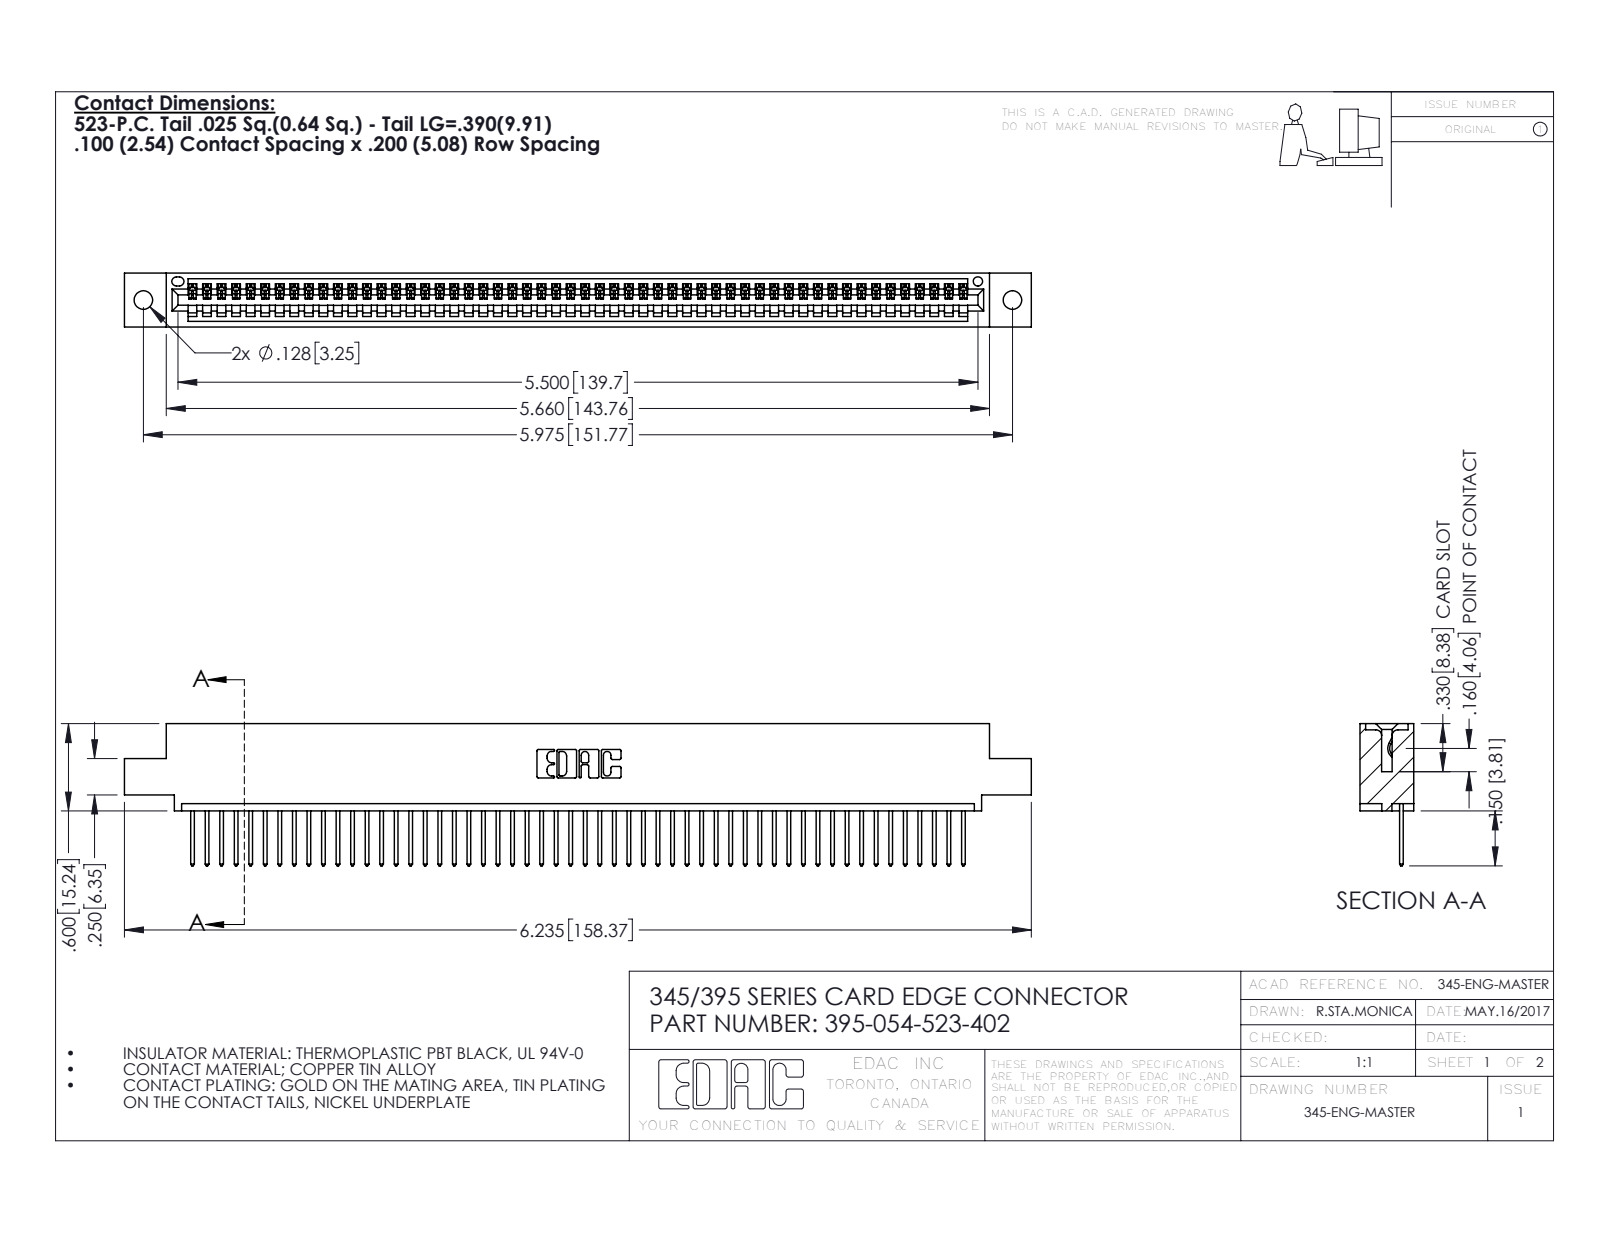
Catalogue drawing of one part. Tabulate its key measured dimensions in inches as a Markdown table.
| quantity | value |
| --- | --- |
| part name | 345-292-001_345-293-123; 395-054-523-402; 345 Part_0.110 Offset - 0.128 Dia |
| STEP written by | SolidWorks 2016 (CONFIG_CONTROL_DESIGN) |
| units | inches |
| bodies | 55 solids, 3262 faces (2244 planar, 1018 cylindrical, 0 other) |
| overall size | 6.235 × 0.977 × 0.37 |
| volume | 0.916 in³ |
| surface area | 30.97 in² |
| round holes (diameter × count) | 0.128 × 2, 0.064 × 1 |
| partial cylindrical surfaces (radius × count) | 0.006 × 108, 0.01 × 108, 0.01 × 22, 0.007 × 6, 0.031 × 6, 0.026 × 3, 0.031 × 2, 0.04 × 2 |
| main face-to-face distances | 0.298, 0.072, 0.37, 0.098, 0.272, 0.025, 0.2, 0.225, 0.149, 0.072 |
| hole center spacings | 0.27, 5.739, 5.975 |
